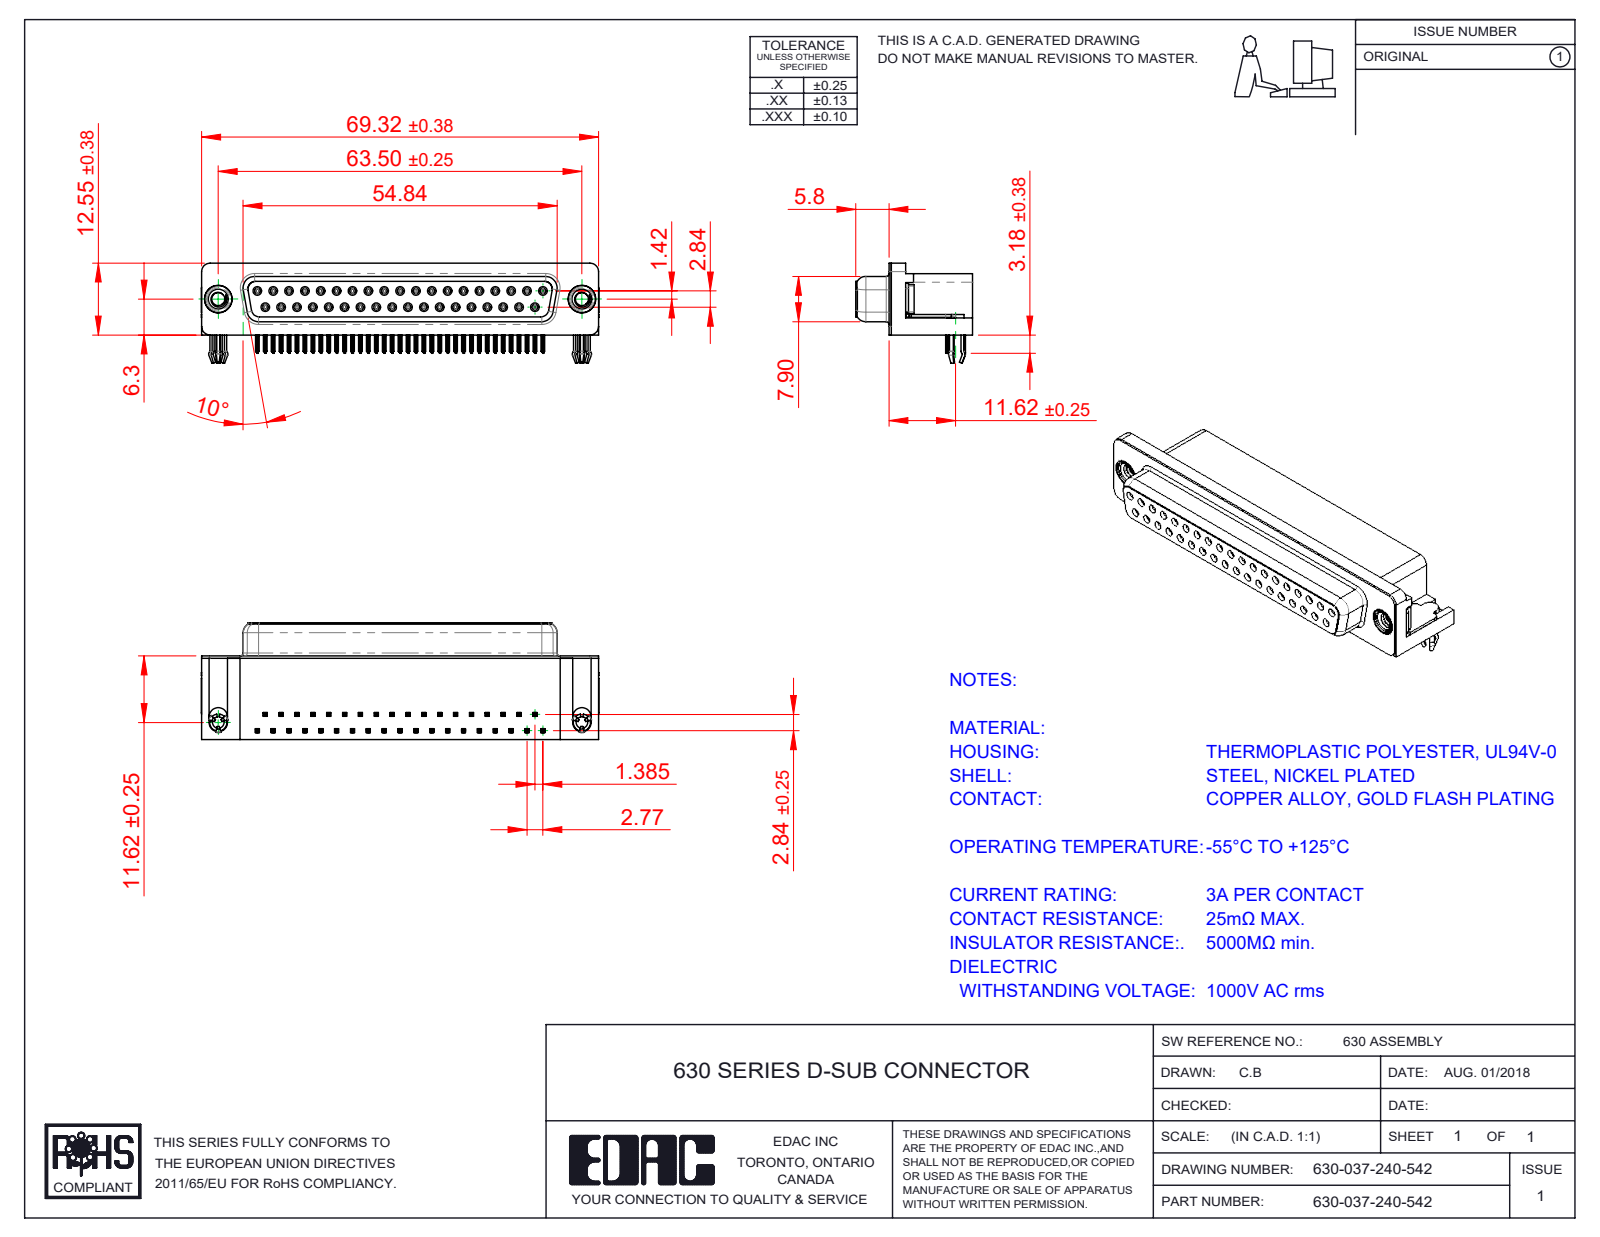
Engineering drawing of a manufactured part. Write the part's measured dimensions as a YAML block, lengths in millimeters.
part_name: "630 Shell_37 Socket; 630 3 Prong Board Lock; 630 Housing_37 Socket; 630 Contact Top (+3 more)"
step_written_by: "SolidWorks 2020 (CONFIG_CONTROL_DESIGN)"
units: millimeters
bodies: {solids: 43, faces: 5664, planar: 2540, cylindrical: 1304, other: 1820}
overall_size: [69.4, 20.4, 17.48]
volume: 11828
surface_area: 13627
round_holes:
  - {diameter: 0.8, count: 37}
  - {diameter: 0.9, count: 37}
  - {diameter: 2, count: 2}
  - {diameter: 2.26, count: 2}
  - {diameter: 4, count: 2}
  - {diameter: 4.8, count: 2}
  - {diameter: 5, count: 2}
round_bosses_or_shafts:
  - {diameter: 1.2, count: 37}
  - {diameter: 4.9, count: 2}
  - {diameter: 4.75, count: 2}
  - {diameter: 3.9, count: 2}
  - {diameter: 3, count: 2}
partial_cylinders:
  - {radius: 0.1, count: 296}
  - {radius: 0.15, count: 148}
  - {radius: 0.35, count: 74}
  - {radius: 0.34, count: 37}
  - {radius: 0.28, count: 18}
  - {radius: 1, count: 18}
  - {radius: 0.25, count: 12}
  - {radius: 1.35, count: 8}
face_to_face_distances: [0.4, 6.2, 10.34, 14.2, 2.84, 6.65, 0.85, 0.45, 14.6, 2.9]
hole_center_spacings: [3.16, 2.77, 5.54, 8.31, 11.08, 13.85, 16.62, 19.39]
